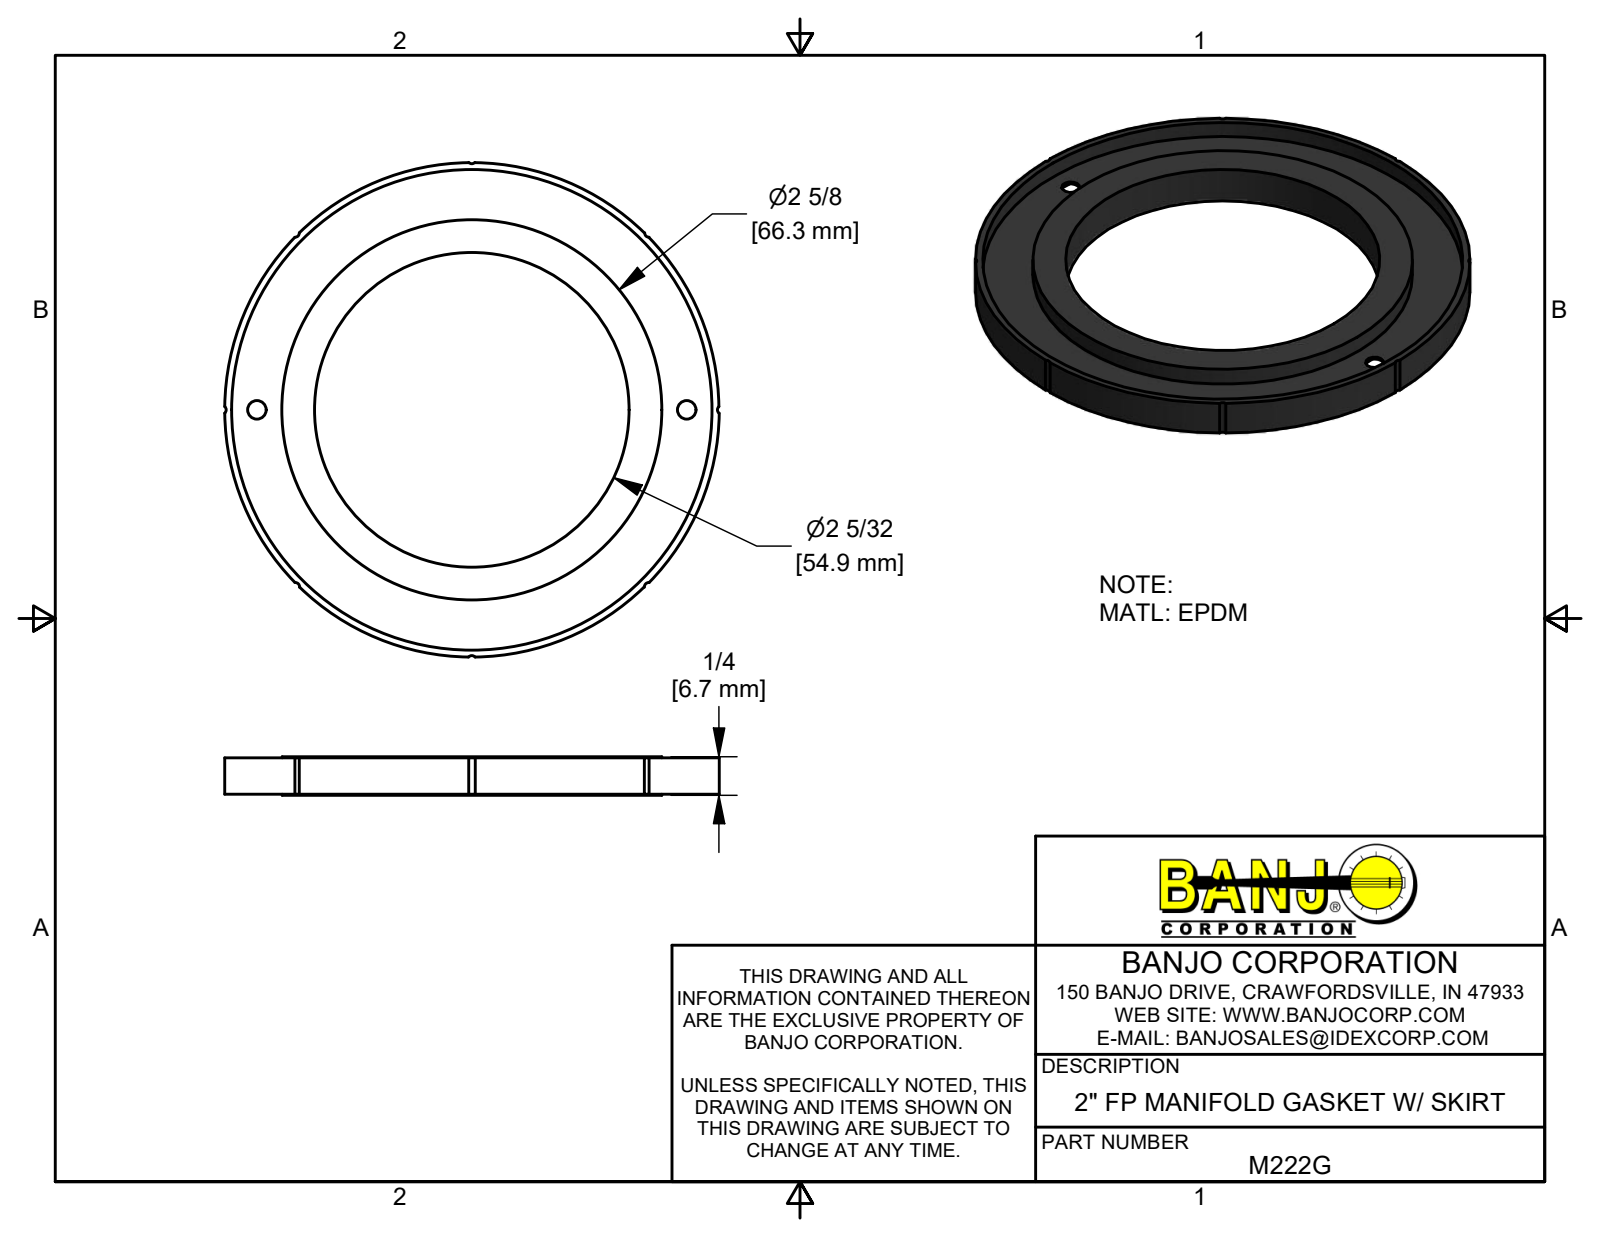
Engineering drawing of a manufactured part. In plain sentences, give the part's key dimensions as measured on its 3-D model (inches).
The part is named "M222G". Its 3-D file was written by "Autodesk Inventor 2019 (AUTOMOTIVE_DESIGN)". It is 1 solid with 29 faces: 6 planar, 23 cylindrical and 0 other. Overall it measures 3.4 by 3.4 by 0.265 inches. Its volume is 0.629 cubic inches and its surface area 19.74 square inches. Round holes: 2 of diameter 0.125, 1 of diameter 2.16, 1 of diameter 3.3. Round bosses or shafts: 1 of diameter 3.4, 1 of diameter 2.61. Partial cylindrical surfaces (rounded edges, fillets, slot ends): 8 of radius 0.03. The main face-to-face distances are 0.124, 0.141, 0.016, 0.265, 0.257, 0.117, 0.133, 0.25. The hole center spacings are 1.478, 2.955.
